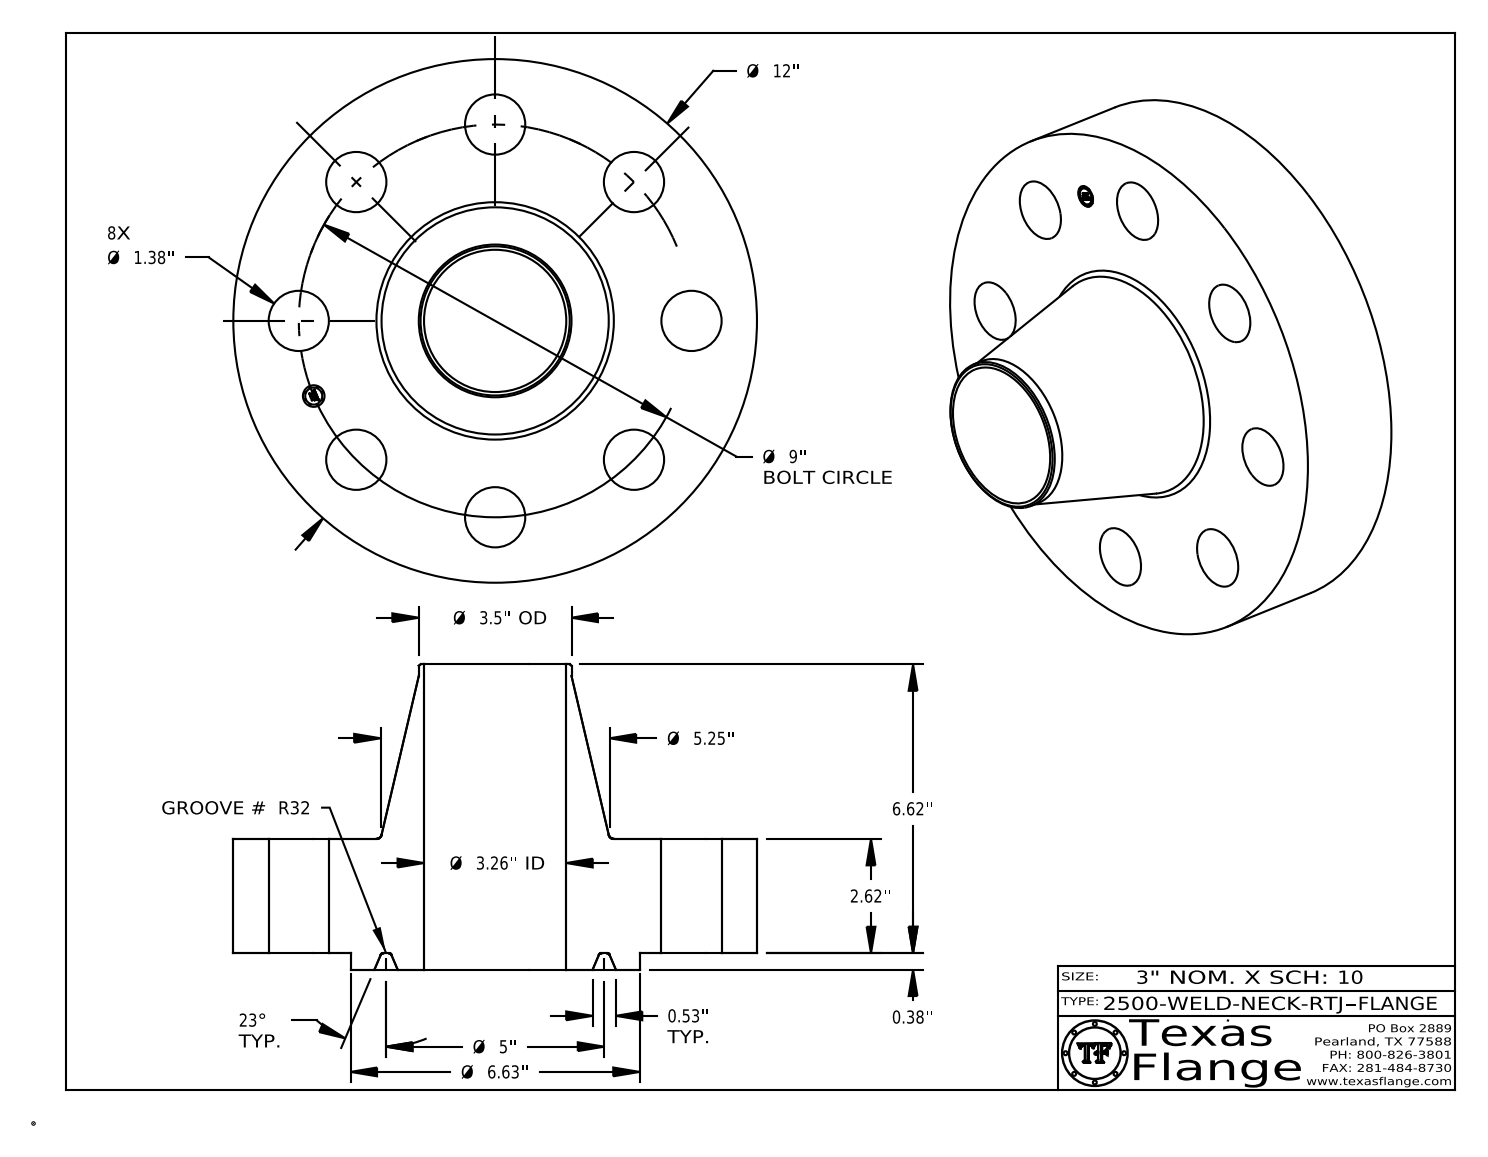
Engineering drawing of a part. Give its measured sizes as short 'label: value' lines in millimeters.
name: 2500-WELD-NECK-RTJ
written by: CATIA V5 STEP AP214 (AUTOMOTIVE_DESIGN)
unit: mm
bodies: 1 solid, 429 faces (371 planar, 44 cylindrical, 14 other)
size: 304.8 × 304.8 × 177.7
volume: 4 536 000 mm³; area: 325 900 mm²
holes: 8× ⌀35.1, 1× ⌀12.6, 1× ⌀82.8
bosses: 8× ⌀0.8, 1× ⌀304.8, 1× ⌀168.3, 1× ⌀88.9, 1× ⌀9.9
face distances: 66.5, 9.5, 76.1, 177.7, 168.1, 101.6, 75.7, 66.2, 0.4, 102
hole spacings: 114.3, 87.5, 161.6, 211.2, 44.6, 127, 190.1, 228.6
